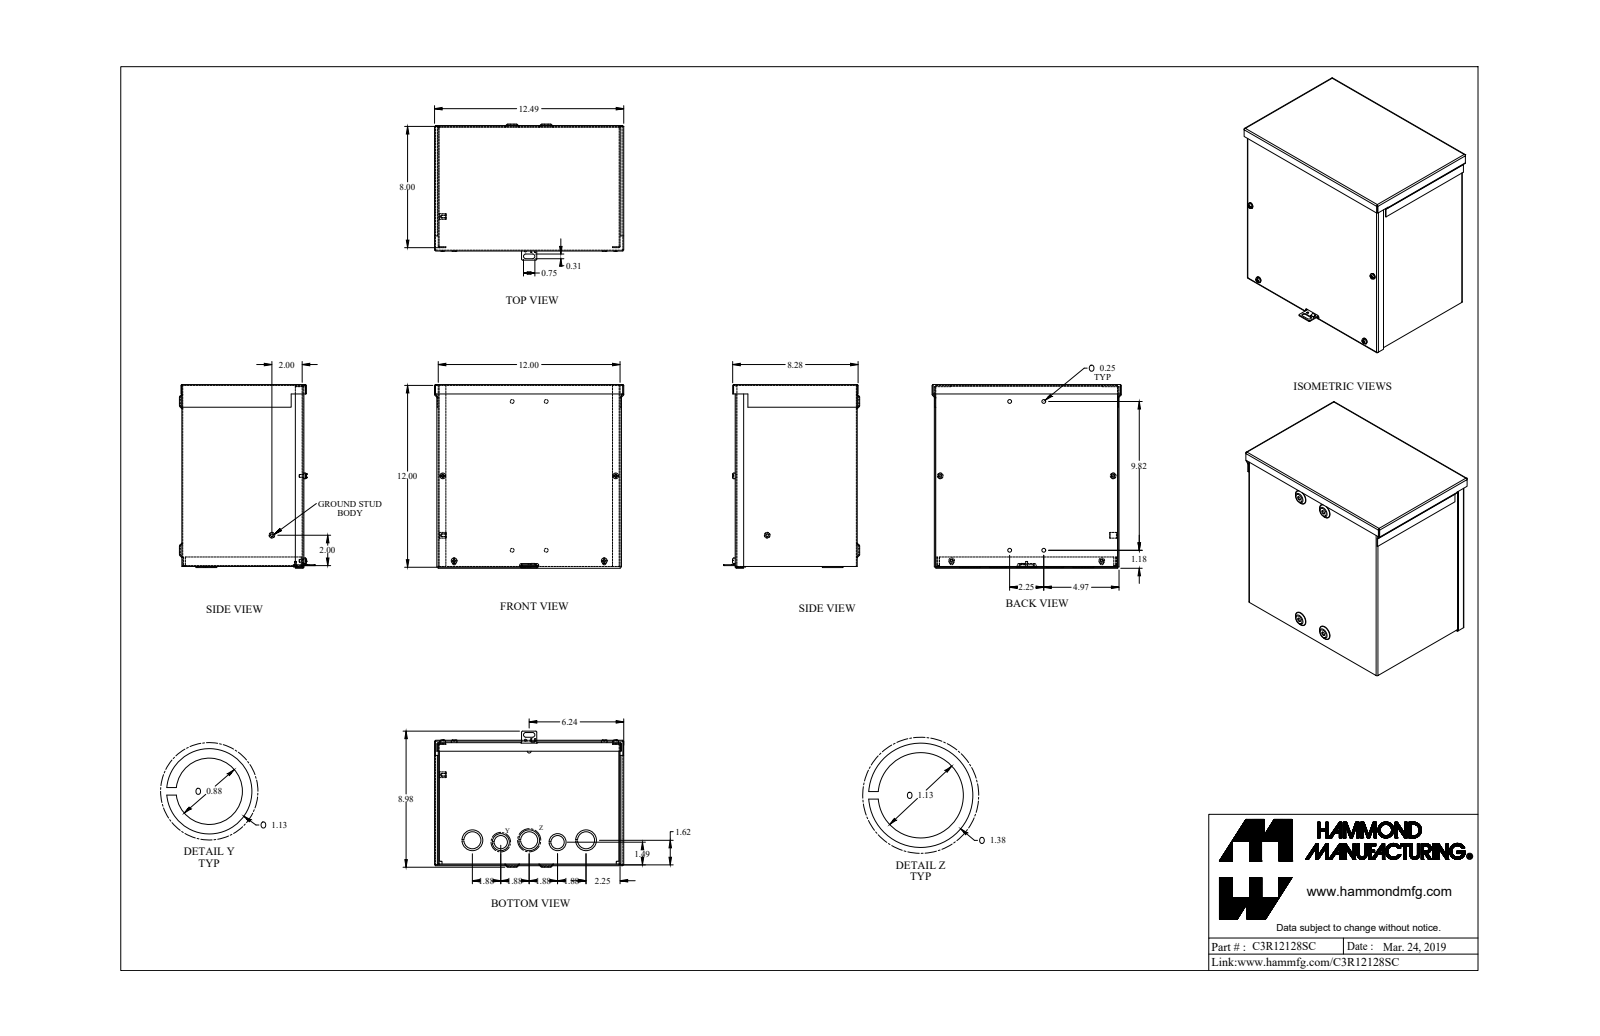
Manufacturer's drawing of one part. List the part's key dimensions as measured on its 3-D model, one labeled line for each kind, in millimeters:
Part name (STEP PRODUCT): C3R12128SC_Default
STEP written by: SolidWorks 2019 (CONFIG_CONTROL_DESIGN)
Units: millimetres
Bodies: 11 solids, 429 faces (226 planar, 117 cylindrical, 86 other)
Overall size (bounding box): 317.2 × 307.8 × 228
Volume: 718 600 mm³ · Surface area: 999 400 mm²
Round holes (diameter × count): ⌀4.3 ×4, ⌀6.4 ×4, ⌀28.6 ×3, ⌀22.2 ×2, ⌀3.2 ×1, ⌀3.5 ×1, ⌀4 ×1
Round bosses / shafts (diameter × count): ⌀4.8 ×4, ⌀34.9 ×3, ⌀9.5 ×3, ⌀28.6 ×2, ⌀9.5 ×2, ⌀3.2 ×1
Partial cylindrical surfaces — rounded edges, fillets, slot ends (radius × count): R0.7 ×21, R2.2 ×21, R2.8 ×8, R3.2 ×8, R4 ×2
Main face-to-face distances: 1.4, 203.2, 303.4, 304.8, 201.8, 204.6, 1.4, 301.9, 301.9, 303.4
Hole centre spacings: 170.6, 213.7, 95.3, 47.7, 47.8, 57.2, 99.6, 145.4
